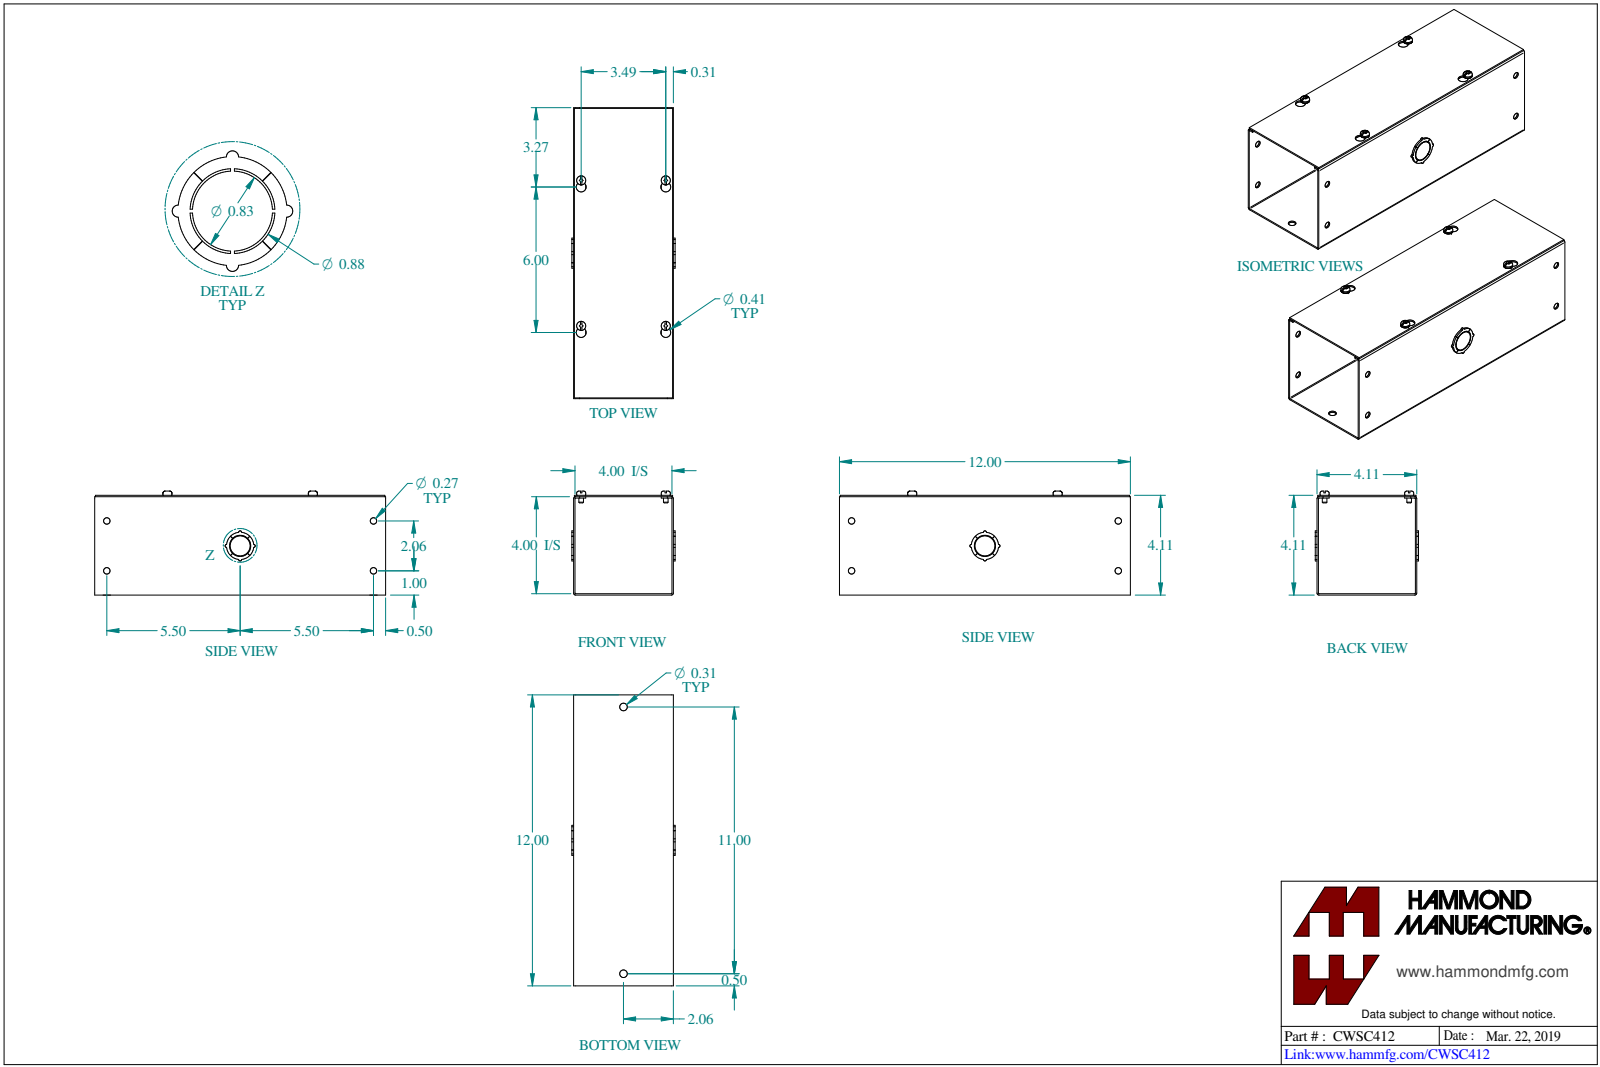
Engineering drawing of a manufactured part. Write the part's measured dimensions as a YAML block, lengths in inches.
part_name: "CWSC412"
step_written_by: "SolidWorks 2023 (CONFIG_CONTROL_DESIGN)"
units: inches
bodies: {solids: 6, faces: 264, planar: 122, cylindrical: 118, other: 24}
overall_size: [12, 4.289, 4.258]
volume: 11.68
surface_area: 411
round_holes:
  - {diameter: 0.177, count: 4}
  - {diameter: 0.266, count: 4}
  - {diameter: 0.313, count: 2}
  - {diameter: 0.875, count: 1}
round_bosses_or_shafts:
  - {diameter: 0.375, count: 4}
  - {diameter: 0.19, count: 4}
  - {diameter: 1.125, count: 1}
  - {diameter: 1.125, count: 1}
  - {diameter: 0.825, count: 1}
partial_cylinders:
  - {radius: 0.029, count: 4}
  - {radius: 0.086, count: 4}
  - {radius: 0.125, count: 4}
  - {radius: 0.203, count: 4}
  - {radius: 0.062, count: 3}
  - {radius: 0.063, count: 1}
face_to_face_distances: [0.057, 4.057, 4, 4.114, 3.943, 0.114, 0.072, 0.129, 4.129, 4.186]
hole_center_spacings: [5.595, 8.677, 11, 2.057, 3.048, 3.049, 3.489, 6]
